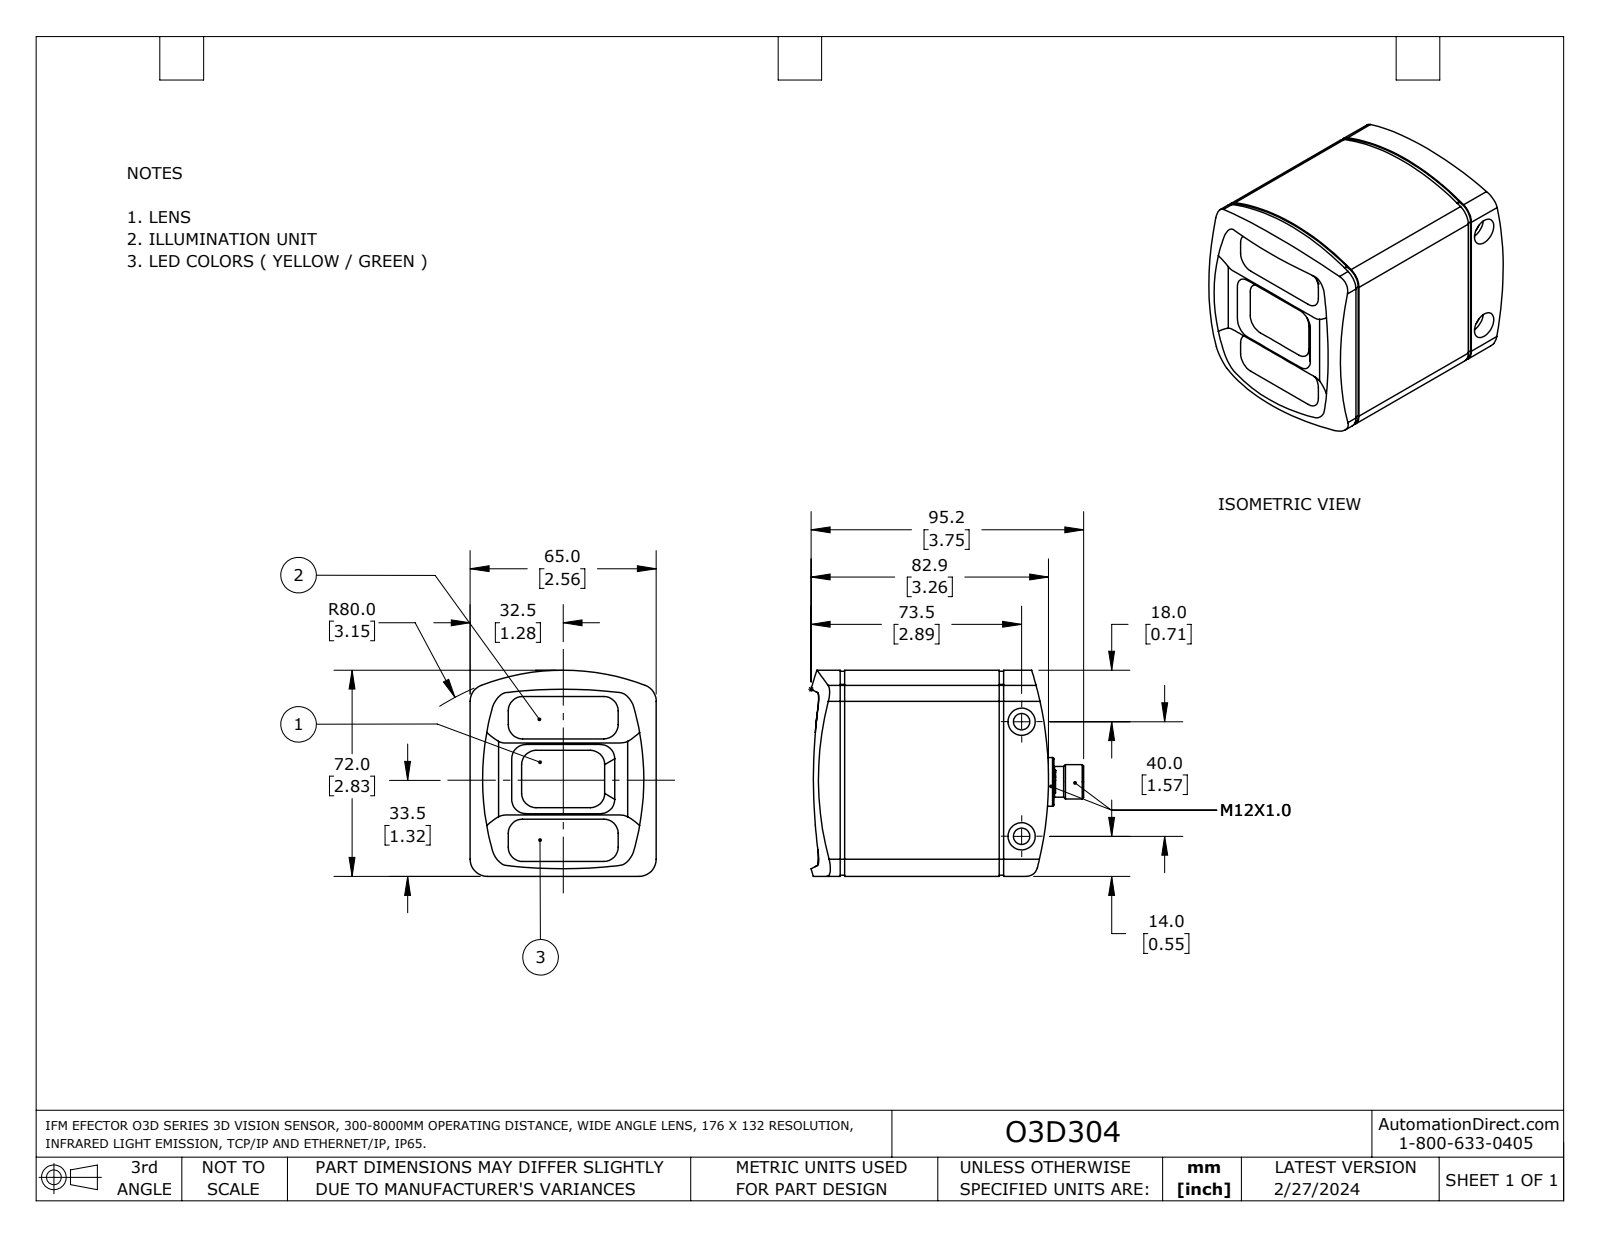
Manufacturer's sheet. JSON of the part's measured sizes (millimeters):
{"part_name": "O3D3xx", "step_written_by": "SolidWorks 2023 (AUTOMOTIVE_DESIGN)", "units": "millimeters", "bodies": {"solids": 1, "faces": 186, "planar": 61, "cylindrical": 104, "other": 21}, "overall_size": [96.5, 72, 65], "volume_mm3": 346300, "surface_area_mm2": 33790, "round_holes": [[7, 4], [5.7, 2], [9.5, 2], [8.3, 1], [8.4, 1], [9.7, 1], [10, 1], [10.8, 1], [10.9, 1], [12.1, 1]], "round_bosses_or_shafts": [[6, 4], [17, 2], [12, 1], [10.7, 1], [8, 1]], "partial_cylinders_radius": [[0.6, 25], [0.2, 24], [5.6, 4], [6, 4], [12, 2], [4, 1], [79.6, 1], [80, 1]], "face_to_face_distances": [65, 0.4, 64.6, 2.8, 5.2, 55.5, 1.5, 79.8, 82.6, 59.8], "hole_center_spacings": [25.6, 27.5, 47.1, 47.4, 48.2, 51, 69.6, 33]}
